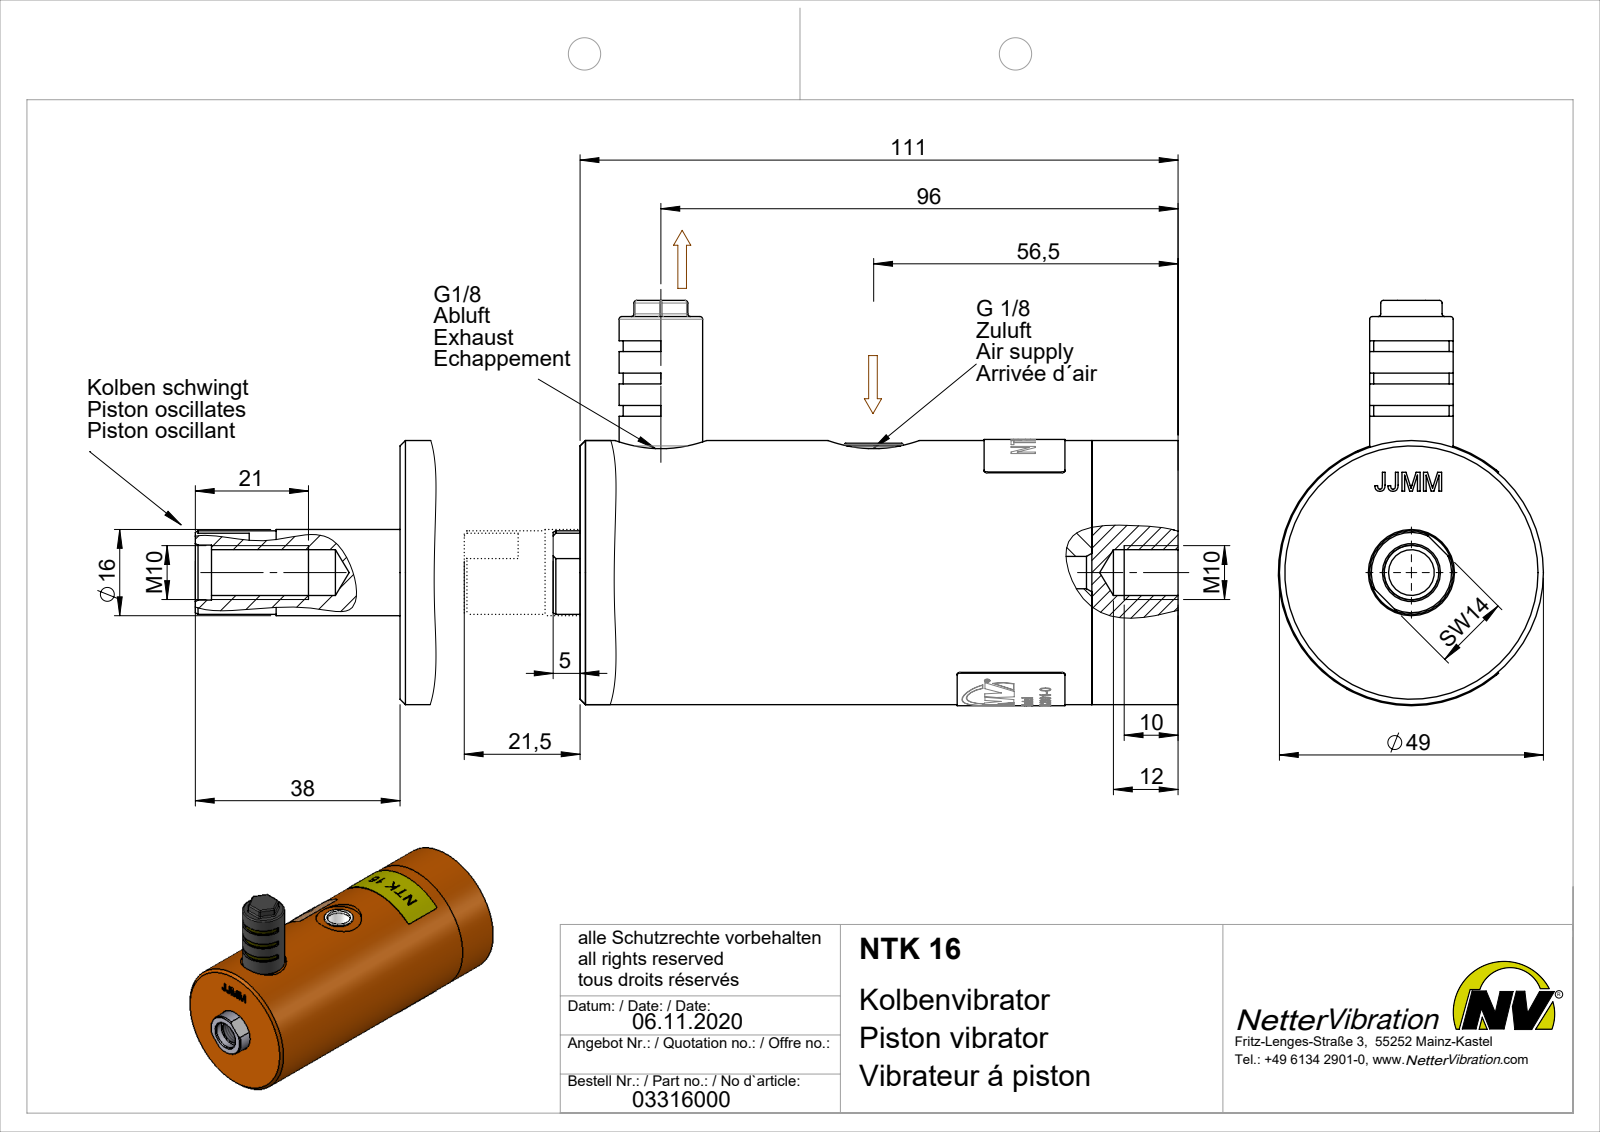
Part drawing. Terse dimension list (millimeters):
name: NTK 16 #03316000
written by: SolidWorks 2015 (AUTOMOTIVE_DESIGN)
unit: mm
bodies: 11 solids, 292 faces (119 planar, 110 cylindrical, 63 other)
size: 116 × 75.2 × 49.2
volume: 218 192 mm³; area: 42 019 mm²
holes: 4× ⌀5, 4× ⌀6.5, 4× ⌀10.5, 2× ⌀8.57, 2× ⌀17, 1× ⌀8.5, 1× ⌀10.2, 1× ⌀16, 1× ⌀49
bosses: 4× ⌀10, 4× ⌀6, 2× ⌀15.5, 1× ⌀9.73
rounds: 30× R0.5, 1× R7, 1× R24.7
face distances: 95, 16, 111, 9.5, 6.5, 104.5, 30, 6, 25, 70
hole spacings: 18, 25.46, 36.01, 39
